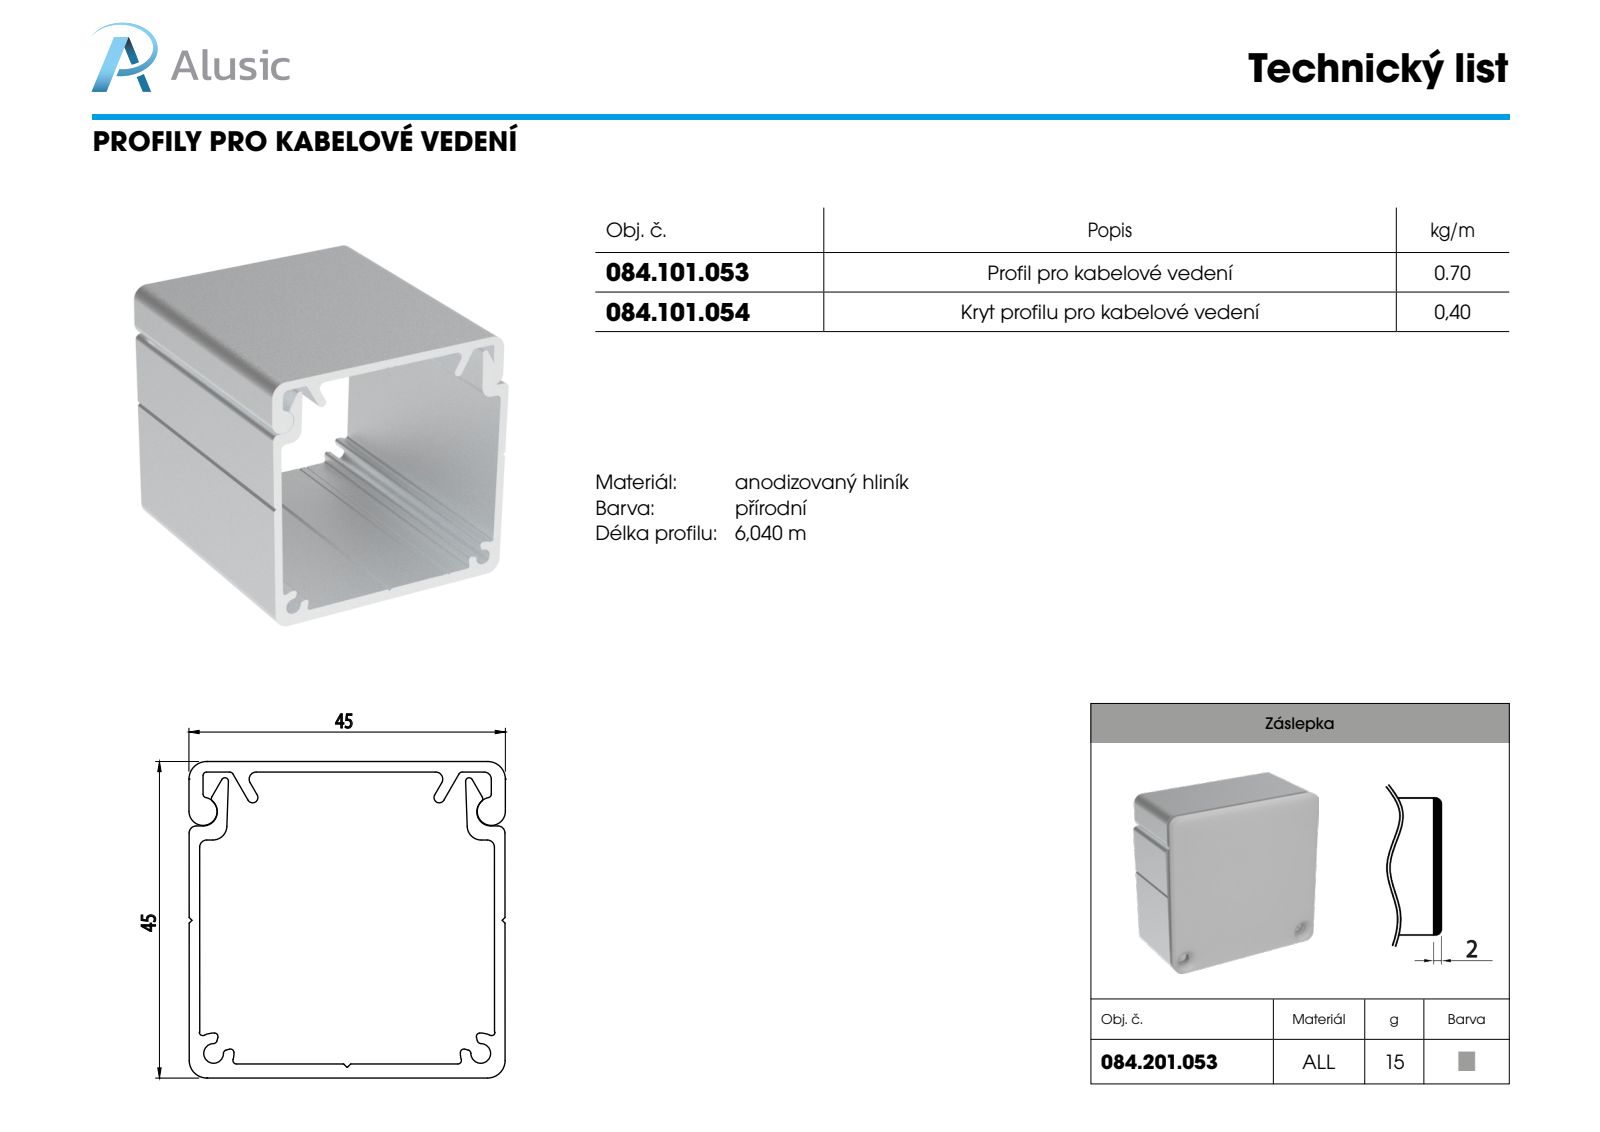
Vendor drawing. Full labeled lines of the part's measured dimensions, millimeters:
Part name (STEP PRODUCT): 084.201.053-L
STEP written by: SolidWorks 2012 (AUTOMOTIVE_DESIGN)
Units: millimetres
Bodies: 1 solid, 14 faces (6 planar, 6 cylindrical, 2 other)
Overall size (bounding box): 45 × 45 × 2
Volume: 3 975 mm³ · Surface area: 4 387 mm²
Round holes (diameter × count): ⌀3.2 ×2
Partial cylindrical surfaces — rounded edges, fillets, slot ends (radius × count): R2.5 ×4
Main face-to-face distances: 2, 45
Hole centre spacings: 38
